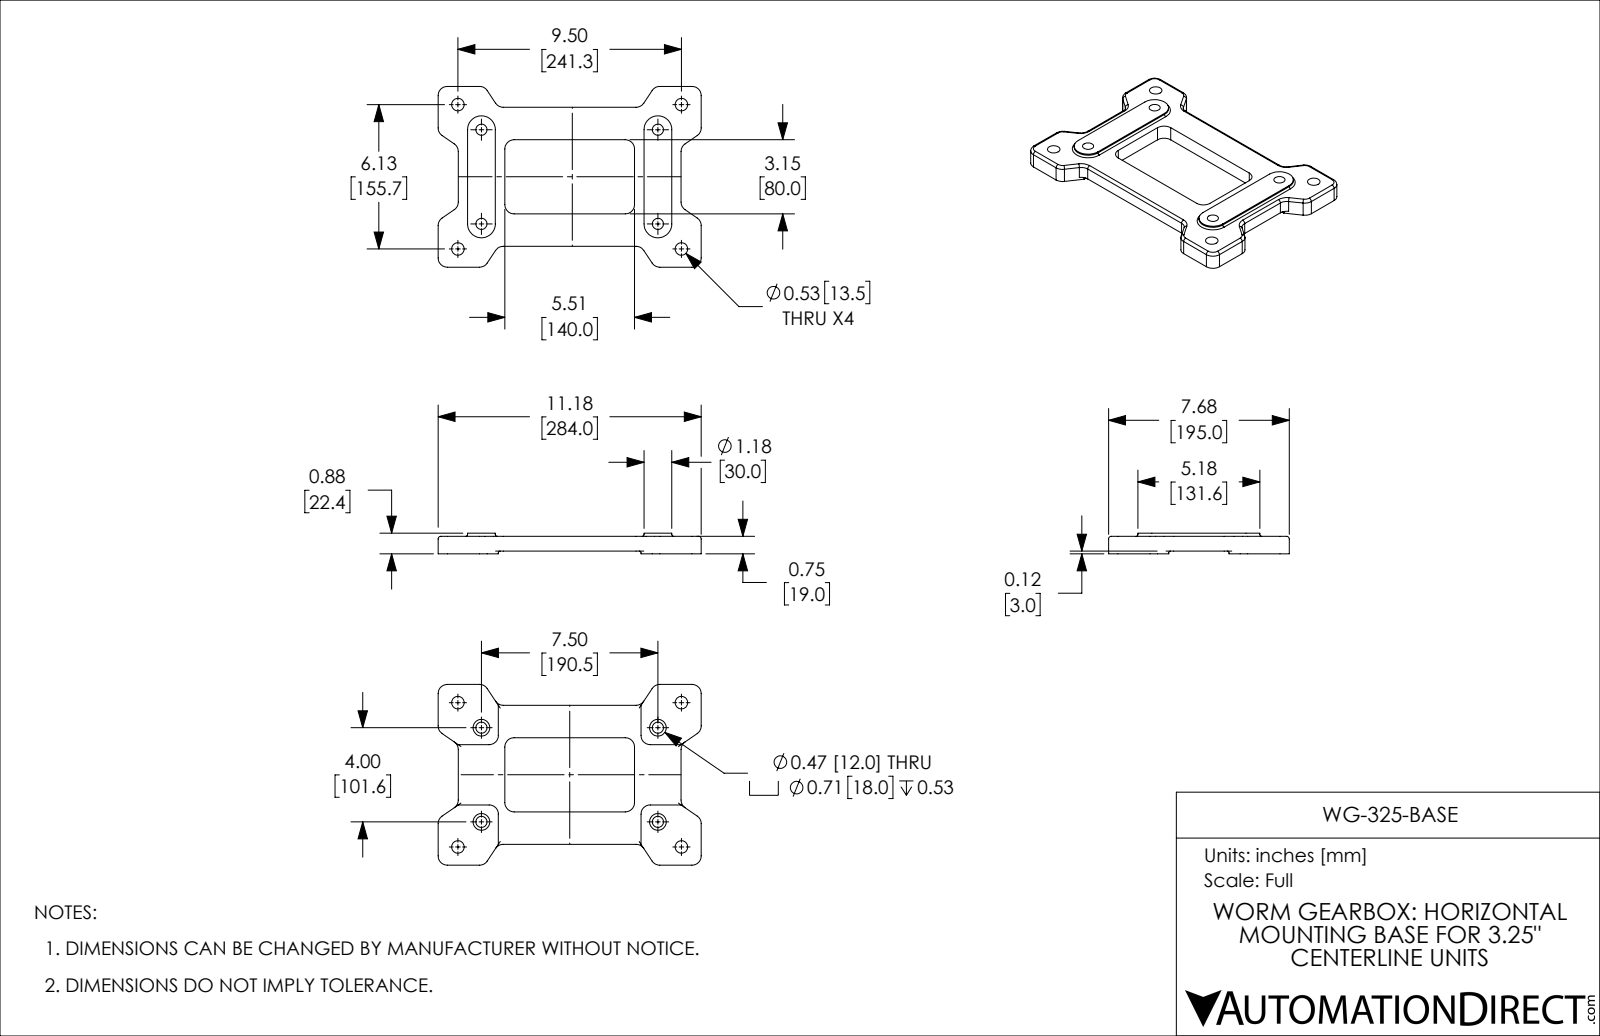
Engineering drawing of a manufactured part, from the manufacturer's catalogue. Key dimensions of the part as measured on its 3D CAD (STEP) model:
Part name (STEP PRODUCT): WG-325-BASE
STEP written by: SolidWorks 2017 (AUTOMOTIVE_DESIGN)
Units: inches
Bodies: 1 solid, 164 faces (48 planar, 88 cylindrical, 28 other)
Overall size (bounding box): 11.181 × 7.677 × 0.882
Volume: 34.87 in³ · Surface area: 151.2 in²
Round holes (diameter × count): ⌀0.472 ×4, ⌀0.531 ×4, ⌀0.709 ×4
Partial cylindrical surfaces — rounded edges, fillets, slot ends (radius × count): R0.394 ×28, R0.118 ×16, R0.079 ×8, R0.591 ×4
Main face-to-face distances: 0.63, 0.118, 0.748, 0.882, 0.764, 0.134, 1.378, 4.528, 0.886, 2.264
Hole centre spacings: 1.461, 5.163, 8.567, 9.894, 4, 6.13, 7.5, 8.5
